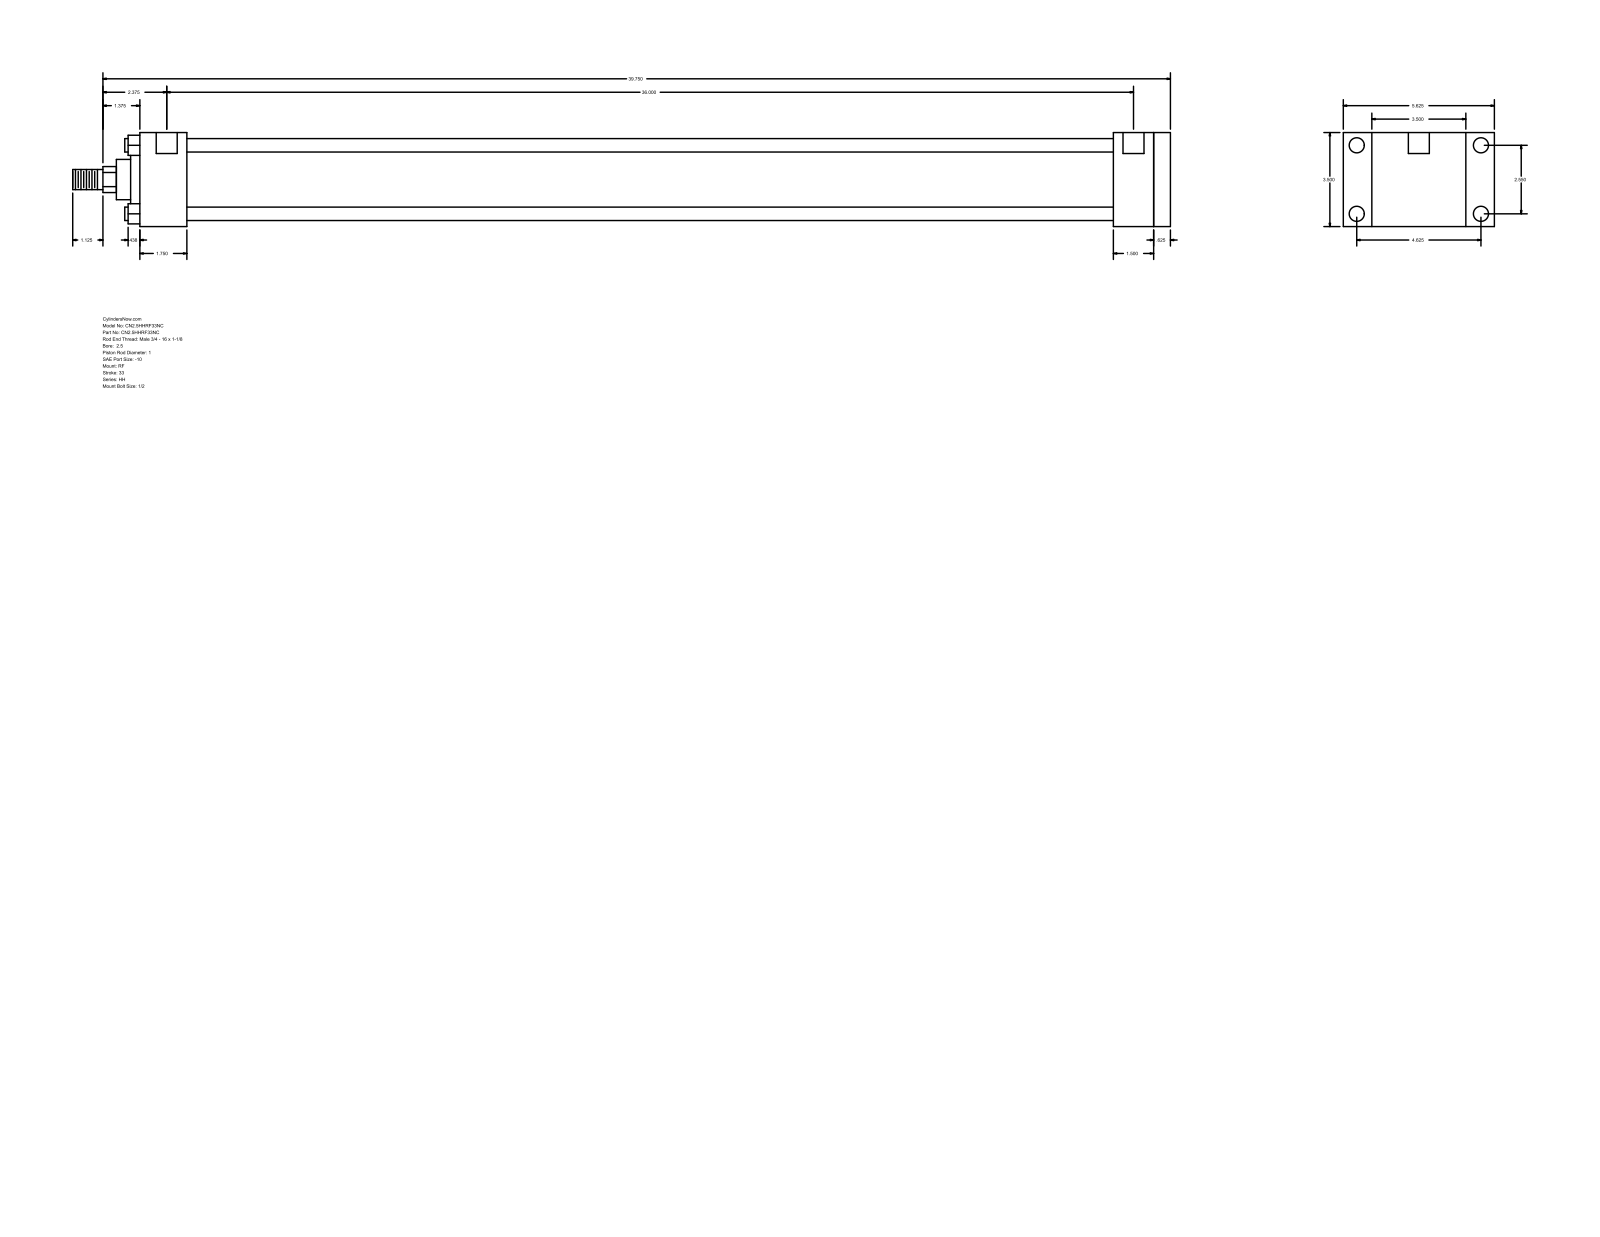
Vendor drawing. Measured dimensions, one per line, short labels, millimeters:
name: HH_RF__0250_1
written by: GSSL Pune (CONFIG_CONTROL_DESIGN)
unit: mm
bodies: 0 solids, 94 faces (65 planar, 29 cylindrical, 0 other)
size: 1038.22 × 142.88 × 88.9
holes: 4× ⌀5.56, 4× ⌀14.3, 2× ⌀19.84
bosses: 4× ⌀12.7, 1× ⌀73.03, 1× ⌀60.33, 1× ⌀38.1, 1× ⌀25.4, 1× ⌀19.05
rounds: 1× R12.29
face distances: 88.9, 15.88, 958.85, 974.73, 38.1, 44.46, 914.39, 930.27, 920.75, 876.29
hole spacings: 64.76, 117.48, 134.15, 917.57, 1.58, 1.59, 914.4, 915.98
